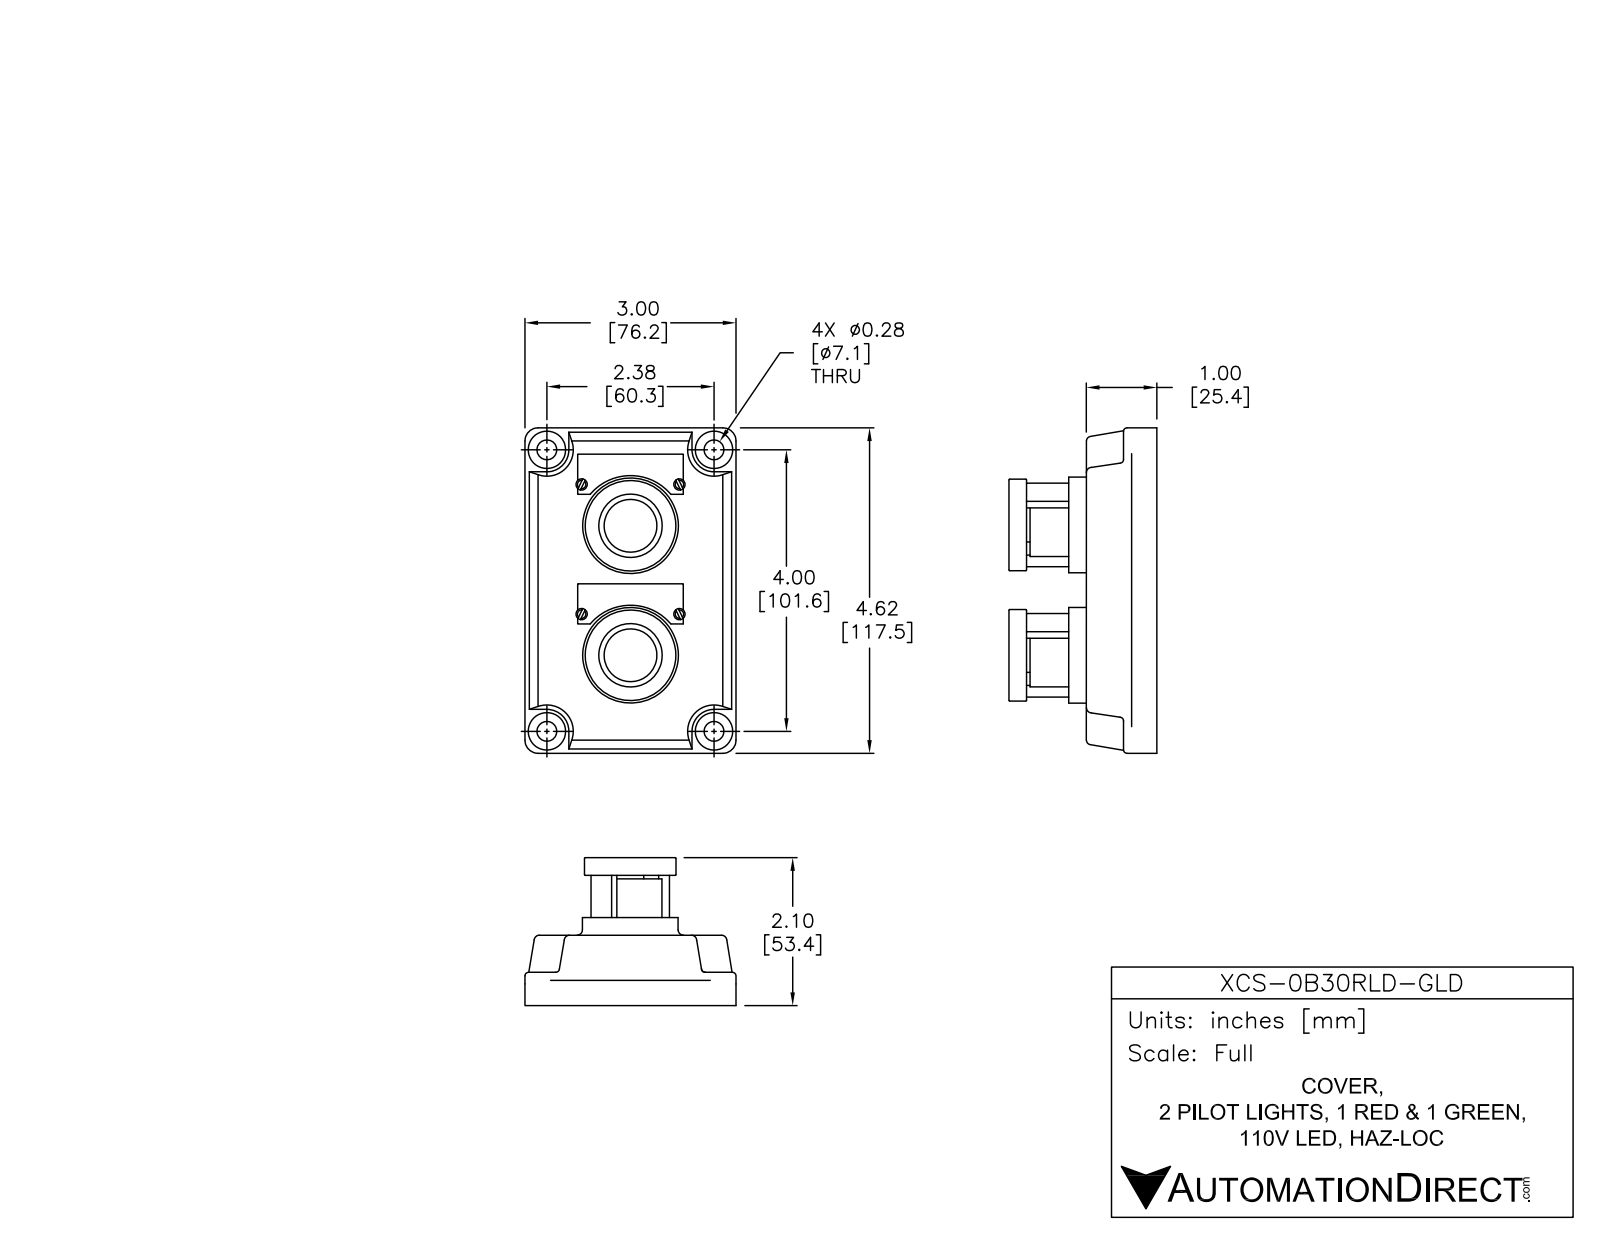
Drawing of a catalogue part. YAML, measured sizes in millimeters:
part_name: "XCS-0B30RLD-GLD"
step_written_by: "SolidWorks 2015 (AUTOMOTIVE_DESIGN)"
units: millimeters
bodies: {solids: 28, faces: 579, planar: 219, cylindrical: 195, other: 165}
overall_size: [117.47, 79.05, 70.32]
volume: 165224
surface_area: 66972
round_holes:
  - {diameter: 7.24, count: 4}
  - {diameter: 6.3, count: 2}
  - {diameter: 17.5, count: 2}
  - {diameter: 22.61, count: 2}
  - {diameter: 32, count: 2}
round_bosses_or_shafts:
  - {diameter: 4.06, count: 8}
  - {diameter: 11.6, count: 4}
  - {diameter: 6.35, count: 4}
  - {diameter: 36.83, count: 2}
  - {diameter: 31.75, count: 2}
  - {diameter: 22, count: 2}
  - {diameter: 15.25, count: 2}
  - {diameter: 10, count: 2}
partial_cylinders:
  - {radius: 1.5, count: 16}
  - {radius: 2, count: 12}
  - {radius: 0.76, count: 8}
  - {radius: 3, count: 8}
  - {radius: 6.35, count: 8}
  - {radius: 1.4, count: 6}
  - {radius: 1.52, count: 6}
  - {radius: 0.51, count: 4}
face_to_face_distances: [26, 1.5, 12.66, 13.34, 11.63, 24.29, 37.63, 10.13, 22.79, 36.13]
hole_center_spacings: [47.5, 0.45, 40.24, 40.32, 80.24, 80.36, 101.6, 117.84]
